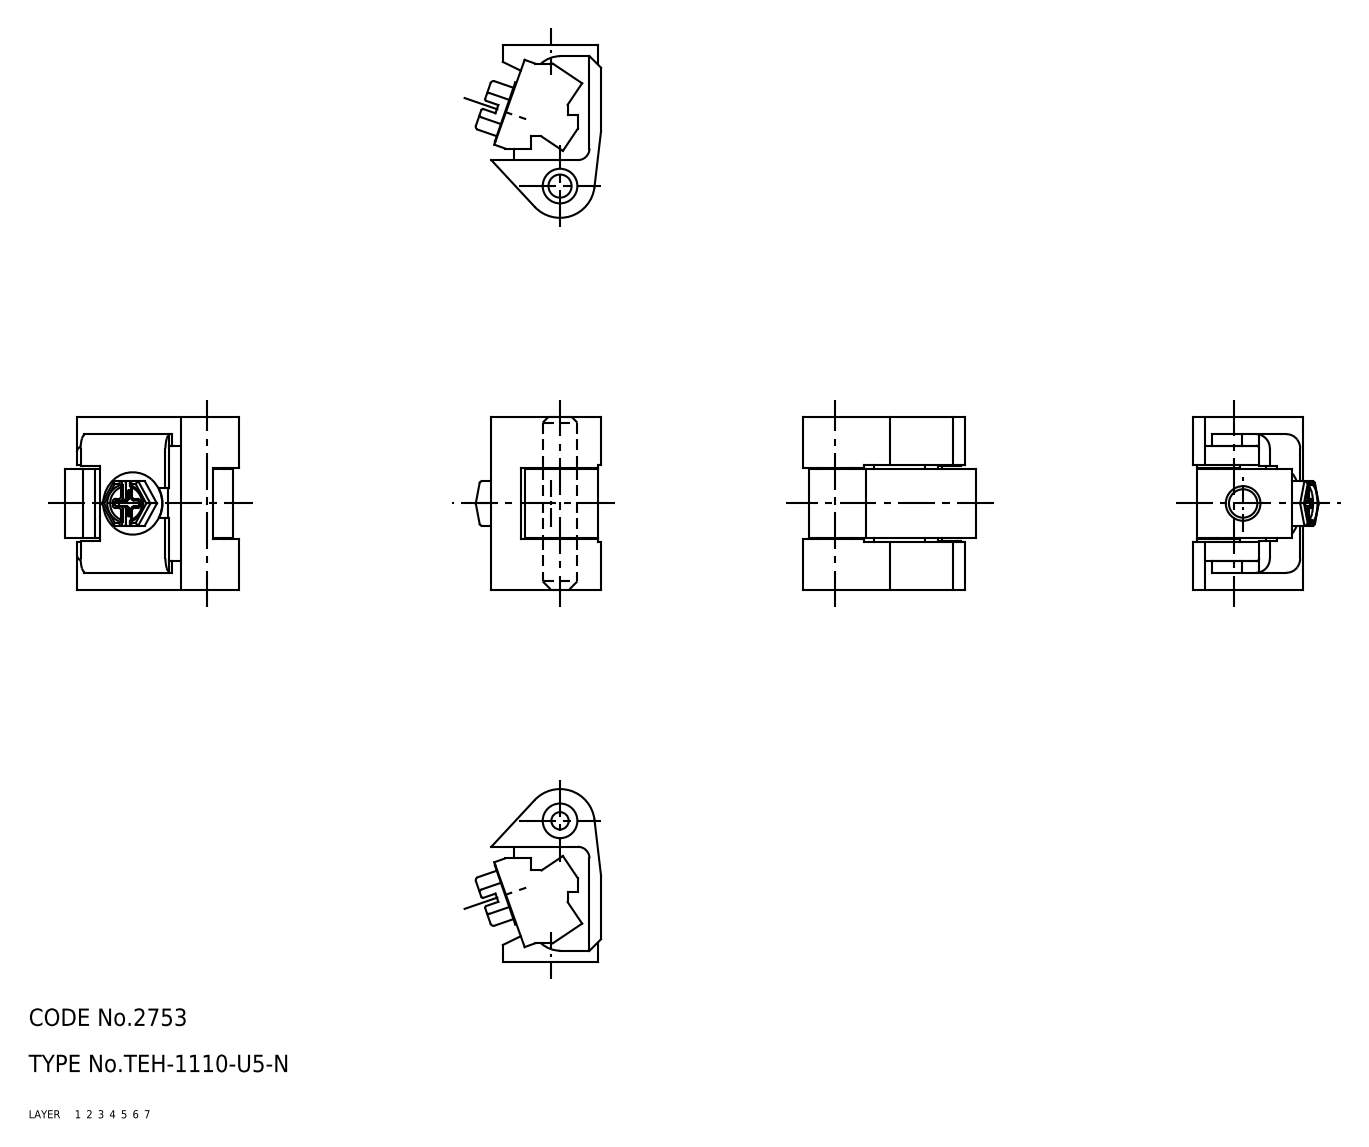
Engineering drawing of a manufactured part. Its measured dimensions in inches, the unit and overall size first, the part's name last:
Units: inches
Overall size (bounding box): 1.181 × 1.181 × 0.871
Volume: 0.569 in³ · Surface area: 12.35 in²
Bodies: 5 solids, 212 faces (0 planar, 0 cylindrical, 212 other)
Part name (STEP PRODUCT): screw; shaft; hinge pieces_B; hinge pieces_A (+2 more)
STEP written by: CADfix (AUTOMOTIVE_DESIGN)
